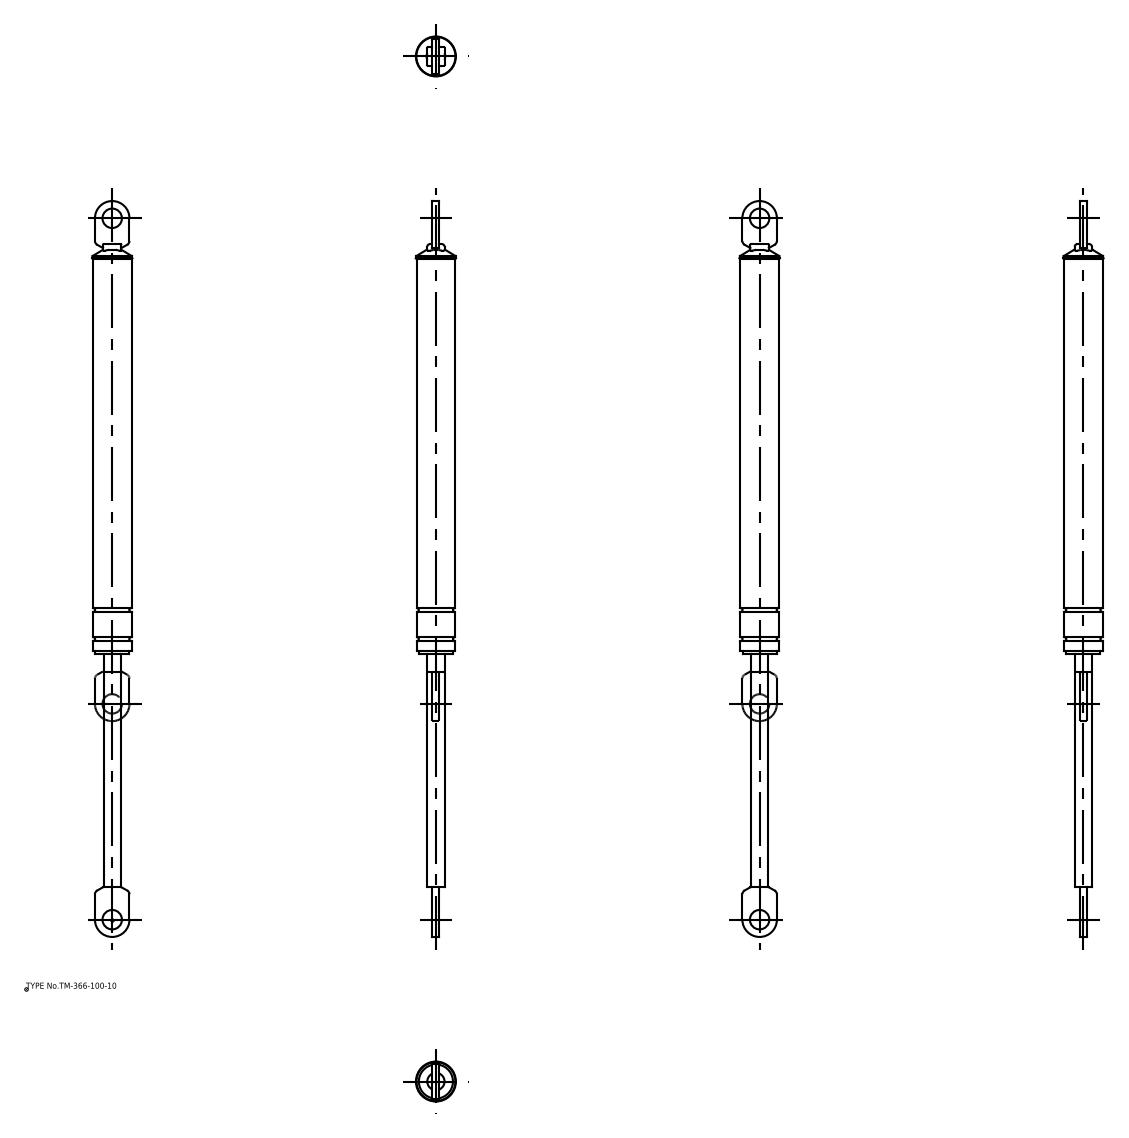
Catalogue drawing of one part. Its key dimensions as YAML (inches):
part_name: "TM_366_100_10; TM_366_100_10_div"
step_written_by: "spGate 16.7.1 (AUTOMOTIVE_DESIGN)"
units: inches
bodies: {solids: 2, faces: 89, planar: 35, cylindrical: 36, other: 18}
overall_size: [13.425, 0.728, 0.728]
volume: 3.316
surface_area: 24.04
round_holes:
  - {diameter: 0.354, count: 2}
round_bosses_or_shafts:
  - {diameter: 0.709, count: 1}
  - {diameter: 0.622, count: 1}
  - {diameter: 0.315, count: 1}
partial_cylinders:
  - {radius: 0.012, count: 8}
  - {radius: 0.079, count: 4}
  - {radius: 0.02, count: 2}
  - {radius: 0.045, count: 2}
  - {radius: 0.315, count: 2}
face_to_face_distances: [0.126, 0.63, 0.067, 4.252, 4.319, 0.146, 0.484, 0.531, 0.071, 0.094]
hole_center_spacings: [12.795]
